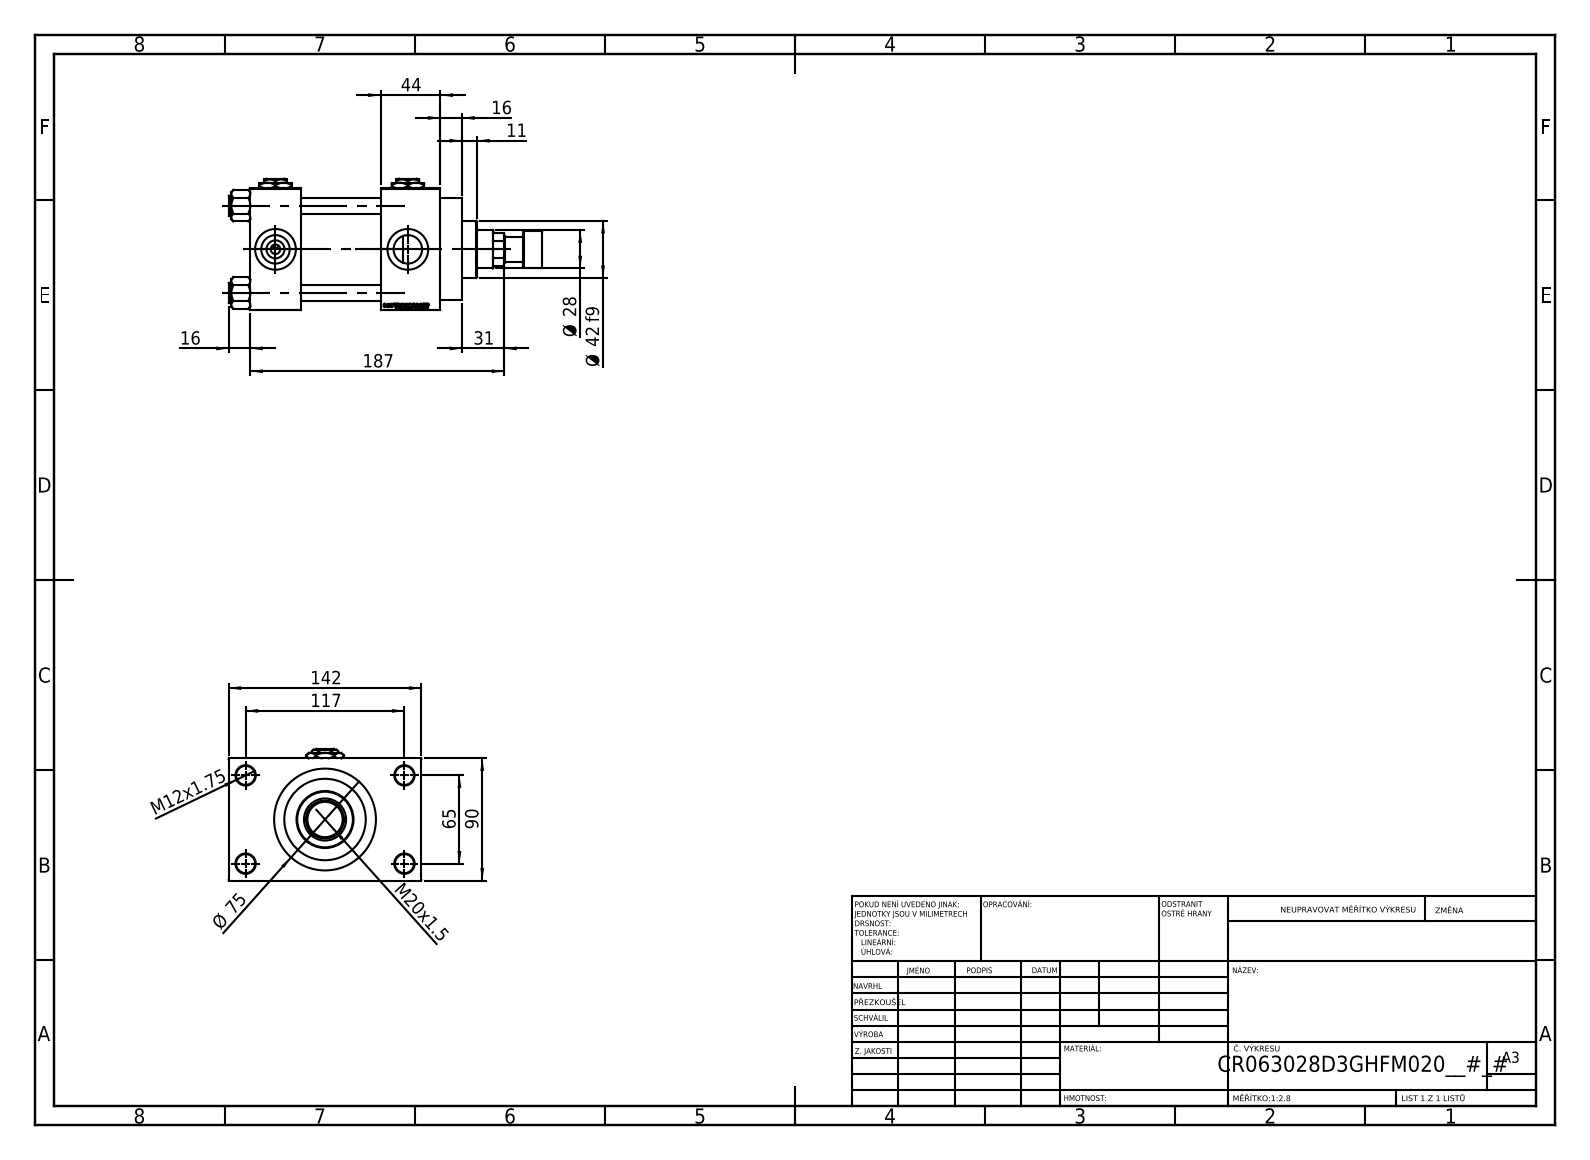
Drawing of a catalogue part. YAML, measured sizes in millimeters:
part_name: "NUT_M5_D; V215CR_ROD_END_F; V215CR_D_TYCINKA; V215CR_D_Body (+3 more)"
step_written_by: "SolidWorks 2019 (CONFIG_CONTROL_DESIGN)"
units: millimeters
bodies: {solids: 14, faces: 1218, planar: 549, cylindrical: 103, other: 566}
overall_size: [231, 142, 97]
volume: 1102000
surface_area: 208198
round_holes:
  - {diameter: 12, count: 4}
  - {diameter: 14, count: 4}
  - {diameter: 20.96, count: 4}
  - {diameter: 30, count: 4}
  - {diameter: 7, count: 3}
  - {diameter: 18.5, count: 1}
  - {diameter: 28, count: 1}
  - {diameter: 31, count: 1}
  - {diameter: 50, count: 1}
  - {diameter: 60, count: 1}
  - {diameter: 63, count: 1}
round_bosses_or_shafts:
  - {diameter: 15, count: 4}
  - {diameter: 75, count: 1}
  - {diameter: 69, count: 1}
  - {diameter: 42, count: 1}
  - {diameter: 27, count: 1}
  - {diameter: 18, count: 1}
face_to_face_distances: [90, 59, 37, 96, 140, 103, 44, 26, 116, 119]
hole_center_spacings: [26.35, 45.47, 64.3, 66.92, 69.81, 90.65, 111.34, 65]
